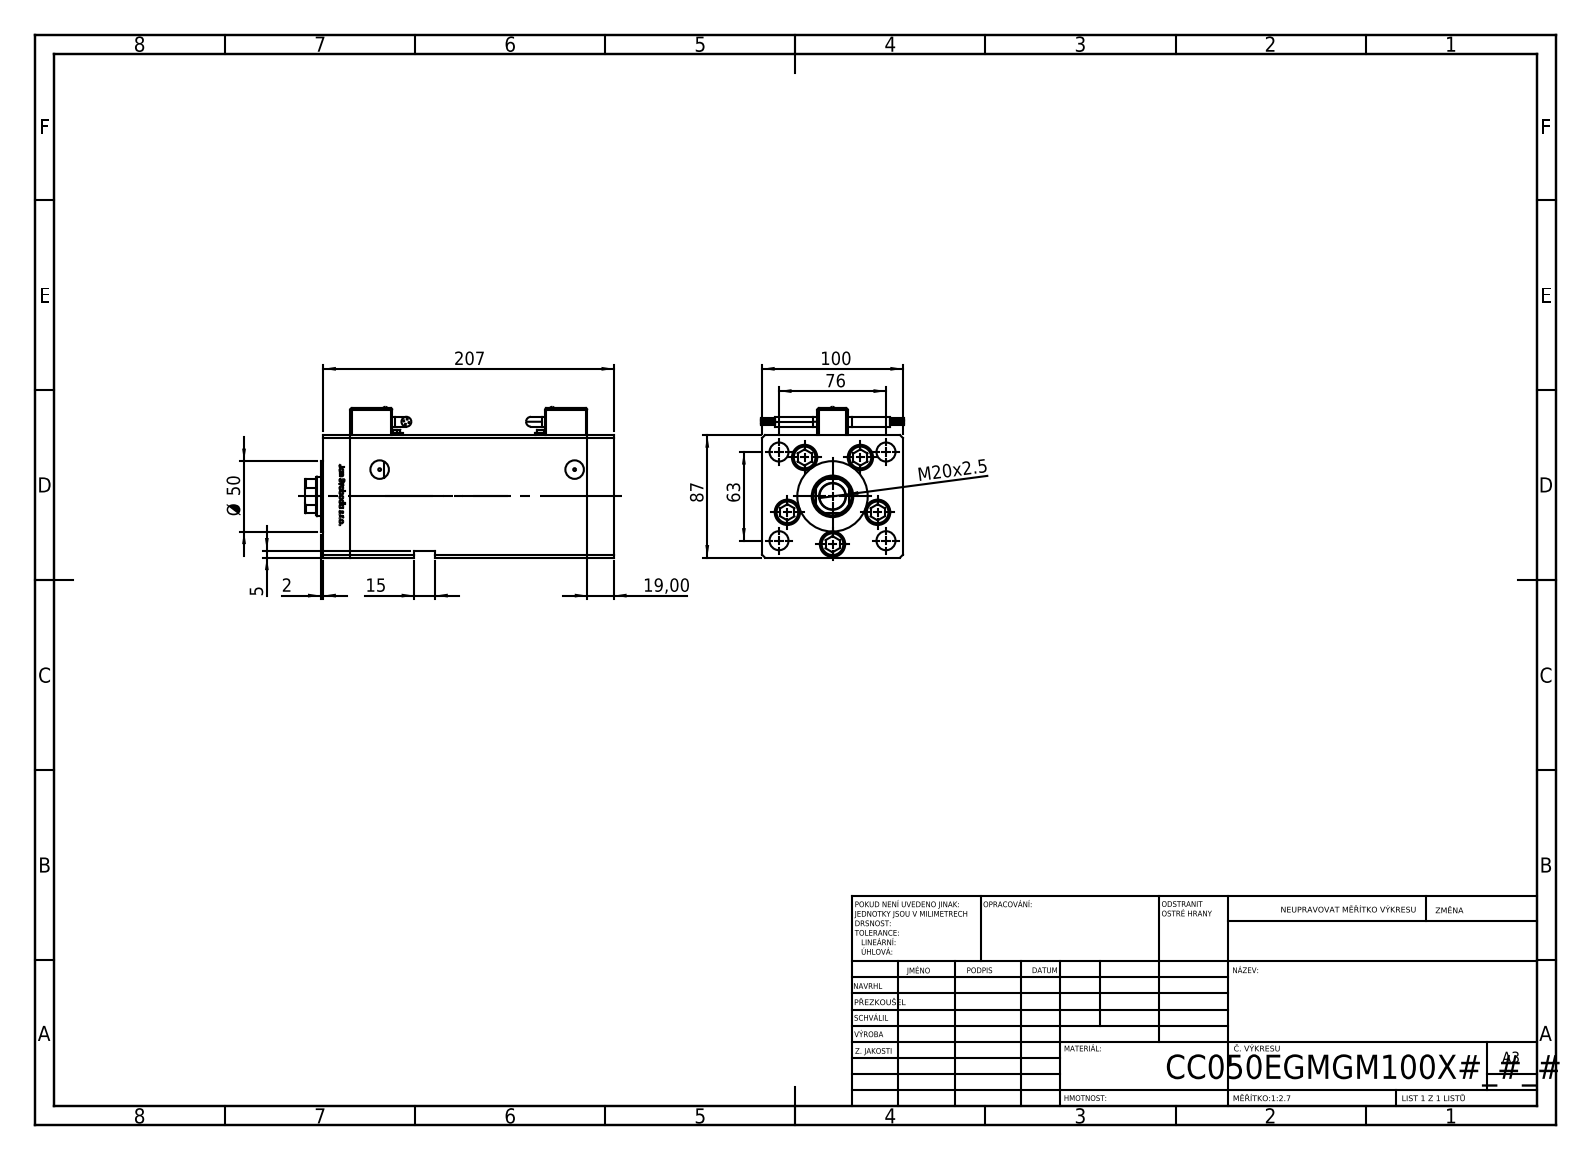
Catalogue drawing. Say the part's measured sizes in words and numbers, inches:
The part is named "V220C_FRONT_E; V220C_E MIDDLE; V220C_VC_E; V220C BACK_E (+2 more)". Its 3-D file was written by "SolidWorks 2019 (CONFIG_CONTROL_DESIGN)". It is 16 solids with 1418 faces: 553 planar, 255 cylindrical and 610 other. Overall it measures 8.642 by 4.217 by 4 inches. Its volume is 94.34 cubic inches and its surface area 378.9 square inches. Round holes: 11 of diameter 0.531, 5 of diameter 0.709, 5 of diameter 0.728, 4 of diameter 0.492, 2 of diameter 0.079, 2 of diameter 0.142, 2 of diameter 0.197, 2 of diameter 0.276, 2 of diameter 0.518, 1 of diameter 1.102, 1 of diameter 1.161. Round bosses or shafts: 8 of diameter 0.033, 5 of diameter 0.669, 5 of diameter 0.315, 4 of diameter 0.276, 2 of diameter 0.236, 2 of diameter 0.138, 2 of diameter 0.098, 1 of diameter 1.969. Partial cylindrical surfaces (rounded edges, fillets, slot ends): 24 of radius 0.039, 4 of radius 0.157, 2 of radius 0.037, 1 of radius 0.531. The main face-to-face distances are 3.937, 3.425, 0.748, 6.634, 7.382, 1.348, 8.13, 0.6, 6.033, 6.781. The hole center spacings are 1.339, 0.732, 1.561, 1.943, 2.281, 0.325, 0.828, 1.499.
